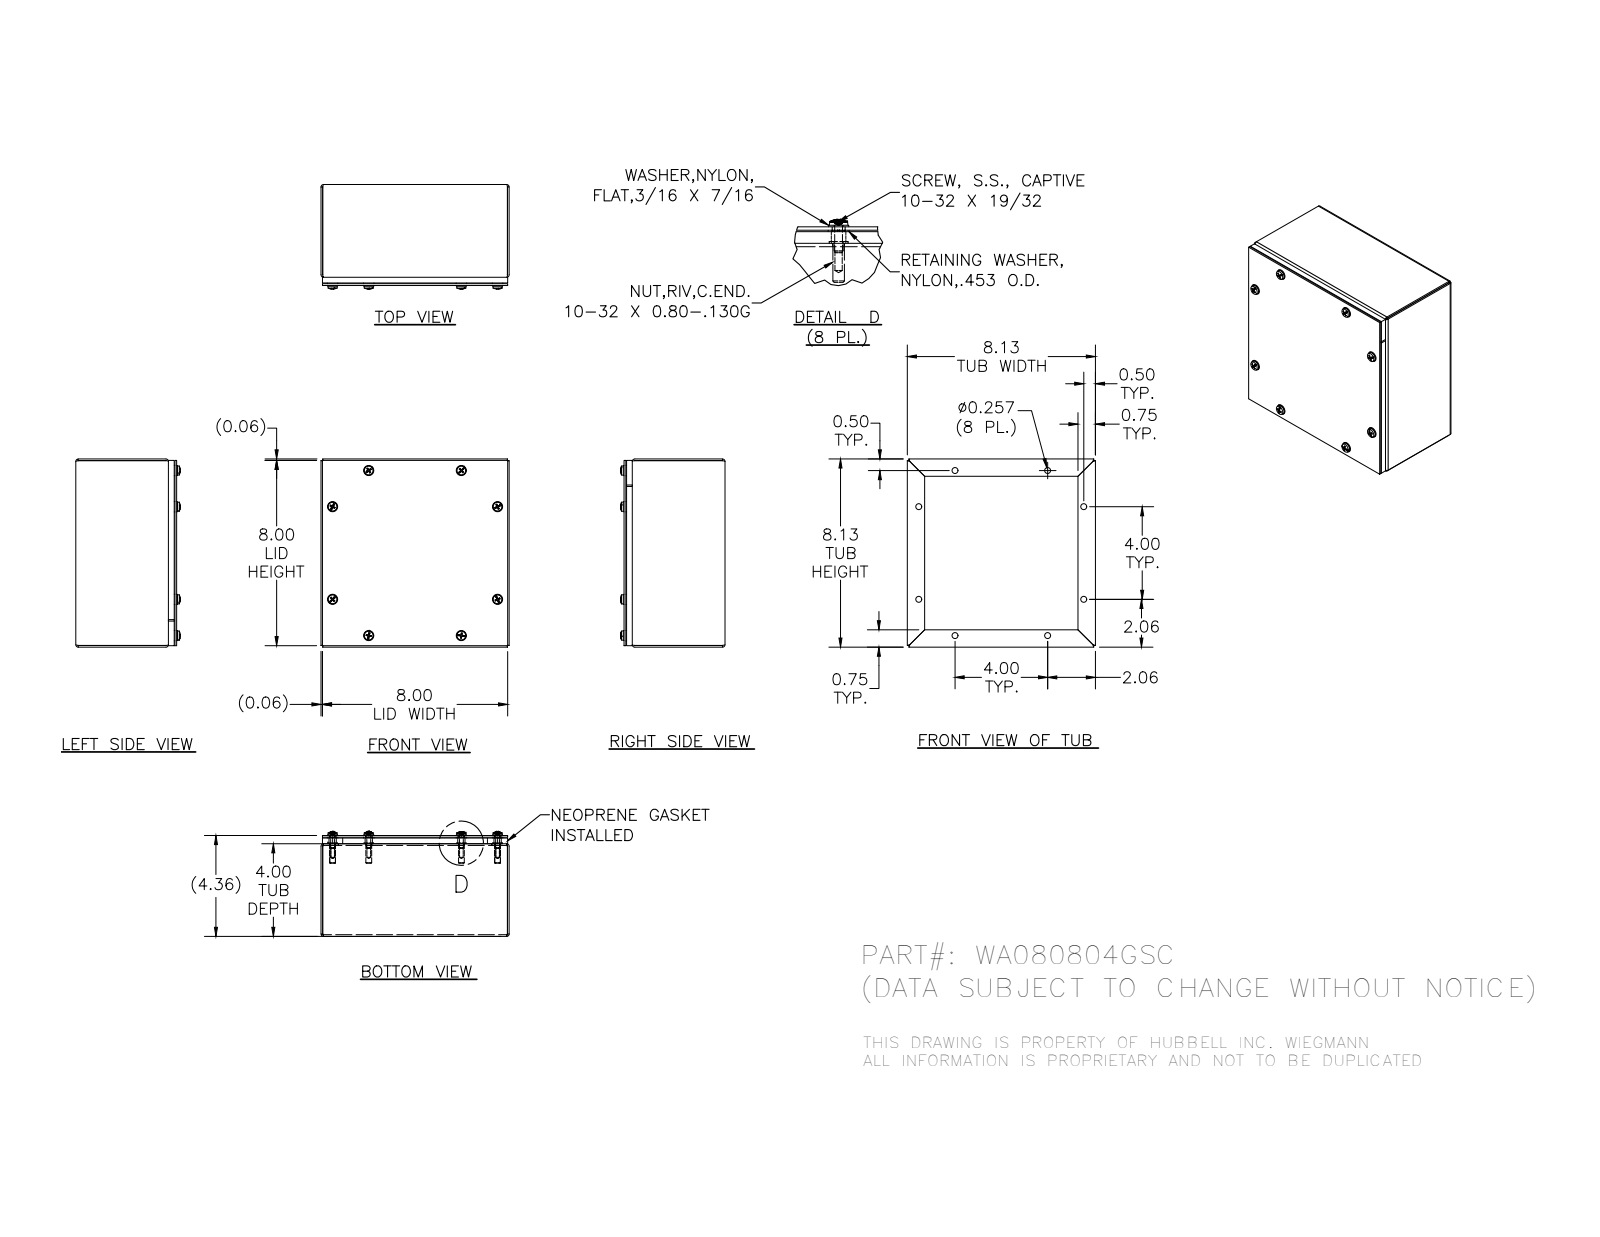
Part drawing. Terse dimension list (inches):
name: 39077; 37210; WA080804GSCBKP; WA080804GSC (+4 more)
written by: SolidWorks 2014 (AUTOMOTIVE_DESIGN)
unit: in
bodies: 36 solids, 892 faces (420 planar, 240 cylindrical, 232 other)
size: 8.125 × 8.125 × 4.511
volume: 26.75 in³; area: 640 in²
holes: 8× ⌀0.156, 8× ⌀0.188, 8× ⌀0.196, 8× ⌀0.257, 8× ⌀0.278, 8× ⌀0.281, 8× ⌀0.313
bosses: 8× ⌀0.453, 8× ⌀0.437, 8× ⌀0.406, 8× ⌀0.248, 8× ⌀0.167
rounds: 8× R0.031, 8× R0.089, 8× R0.105
face distances: 0.074, 4.282, 8.051, 4.208, 4.356, 0.356, 3.926, 8.125, 7.977, 0.282
hole spacings: 4, 5.778, 5.778, 2.209, 5.777, 7.867, 7.866, 2.21
